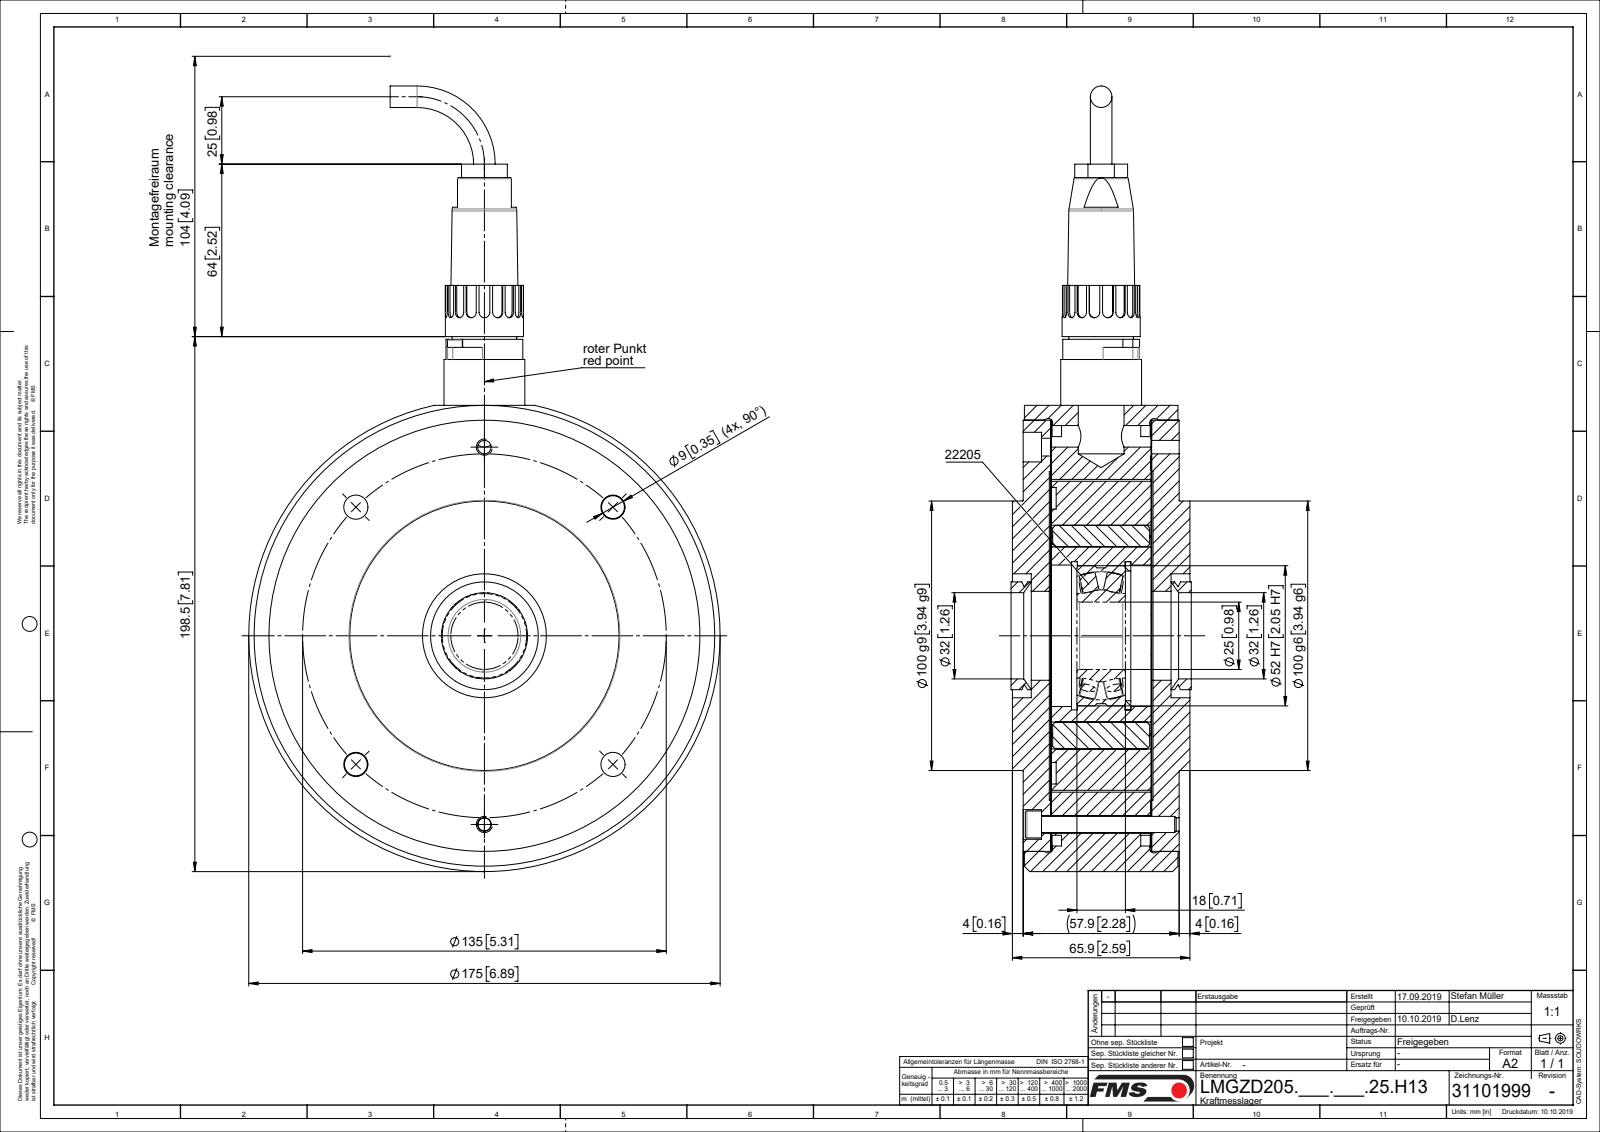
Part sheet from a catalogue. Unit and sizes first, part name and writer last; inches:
Units: inches
Overall size (bounding box): 11.476 × 6.89 × 2.634
Round holes (diameter × count): ⌀0.098 ×6, ⌀0.354 ×4, ⌀0.126 ×3, ⌀0.134 ×2, ⌀0.142 ×2, ⌀0.197 ×2, ⌀0.26 ×2, ⌀0.315 ×2, ⌀0.335 ×2, ⌀0.433 ×2, ⌀0.394 ×1, ⌀0.413 ×1
Round bosses / shafts (diameter × count): ⌀0.085 ×7, ⌀0.217 ×2, ⌀0.118 ×2, ⌀6.89 ×1, ⌀6.299 ×1, ⌀5.827 ×1, ⌀3.937 ×1, ⌀3.701 ×1
Partial cylindrical surfaces — rounded edges, fillets, slot ends (radius × count): R0.079 ×19, R0.004 ×4, R0.118 ×2, R0.167 ×2, R0.295 ×2, R0.354 ×2, R0.433 ×2, R0.819 ×1
Main face-to-face distances: 1.467, 0.402, 0.411, 1.868, 1.878, 1.496, 0.03, 0.382, 1.898, 0.02
Hole centre spacings: 0.64, 0.885, 0.906, 1.926, 2.074, 2.657, 3.758, 3.829
Volume: 82.63 in³ · Surface area: 436.6 in²
Bodies: 51 solids, 839 faces (216 planar, 341 cylindrical, 282 other)
Part name (STEP PRODUCT): Zyl-Schr DIN912_M6x50; 47664_01; 51030-04_stp_01; Kabeldose_Kunstst_7pol_01 (+8 more)
STEP written by: SolidWorks 2018 (CONFIG_CONTROL_DESIGN)
